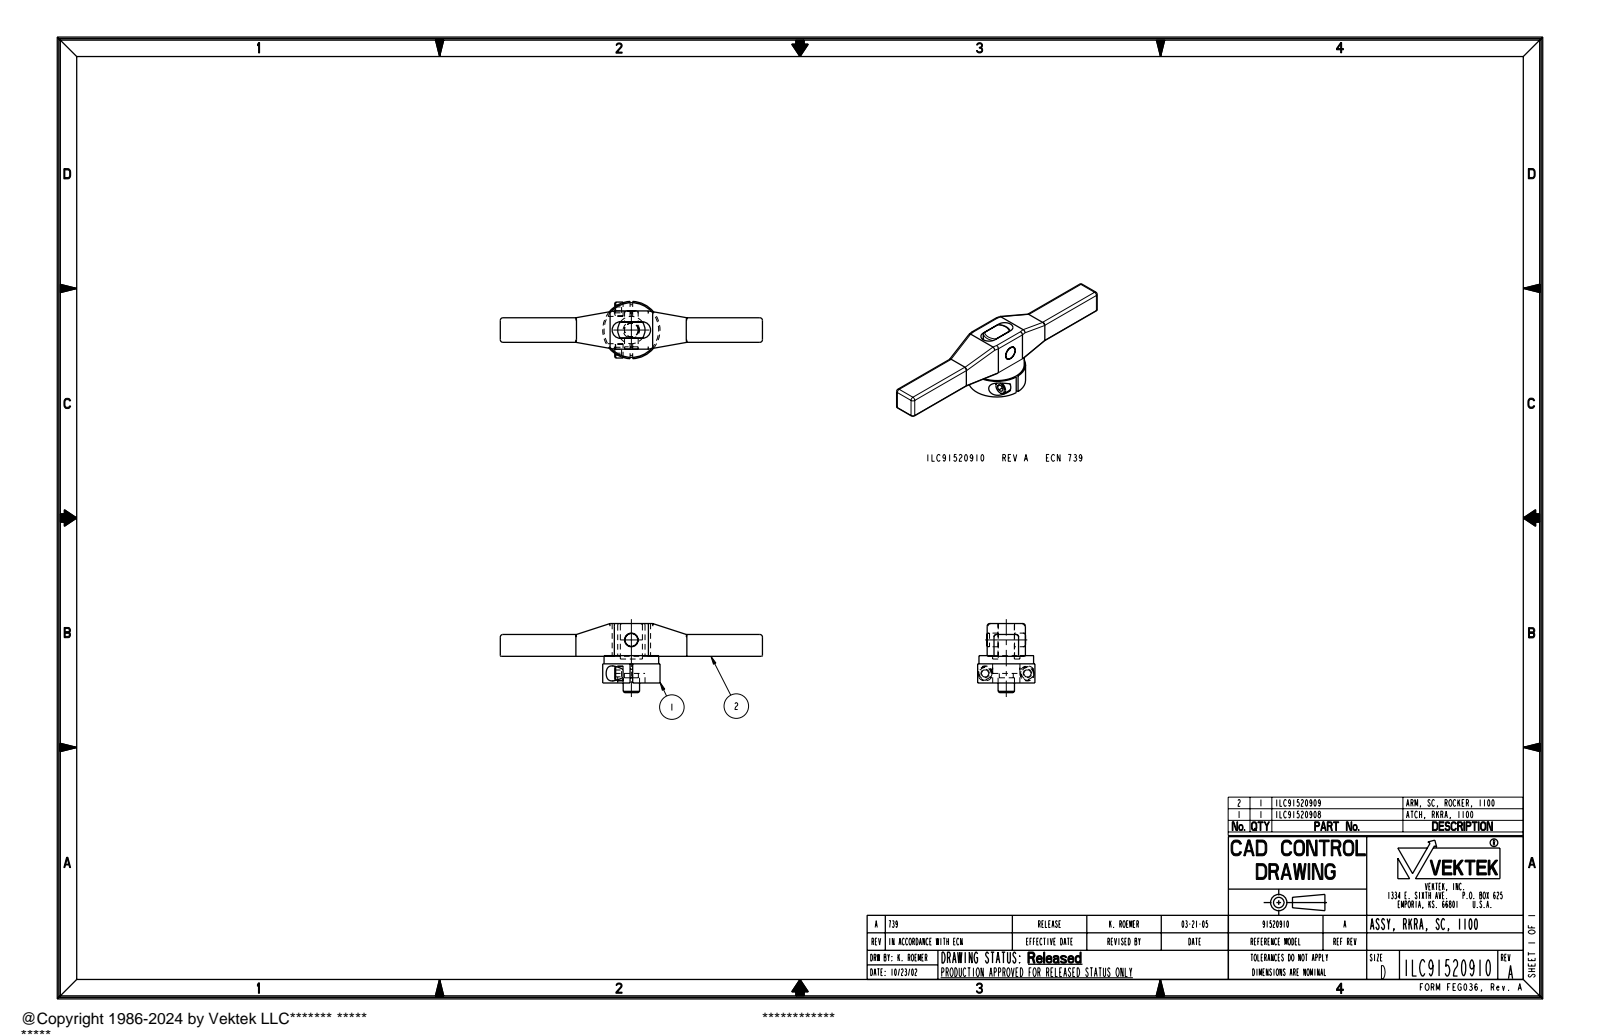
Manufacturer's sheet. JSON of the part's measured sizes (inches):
{"part_name": "ILC91520908; ILC91520909; ILC91520910_ASM", "step_written_by": "PRO/ENGINEER BY PARAMETRIC TECHNOLOGY CORPORATION, 2004290 (AUTOMOTIVE_DESIGN_CC2)", "units": "inches", "bodies": {"solids": 2, "faces": 153, "planar": 61, "cylindrical": 72, "other": 20}, "overall_size": [6, 1.581, 1.311], "volume_in3": 2.98, "surface_area_in2": 25.56, "round_holes": [[0.344, 2], [0.311, 1], [0.625, 1]], "round_bosses_or_shafts": [[0.312, 2], [0.19, 2], [1.312, 1], [1.25, 1], [0.375, 1], [0.32, 1], [0.313, 1]], "partial_cylinders_radius": [[0.06, 22], [0.02, 10], [0.189, 2]], "face_to_face_distances": [0.5, 0.562, 0.61, 1.11, 0.998, 0.626, 0.016, 0.484, 0.156, 0.719], "hole_center_spacings": [0.968]}
